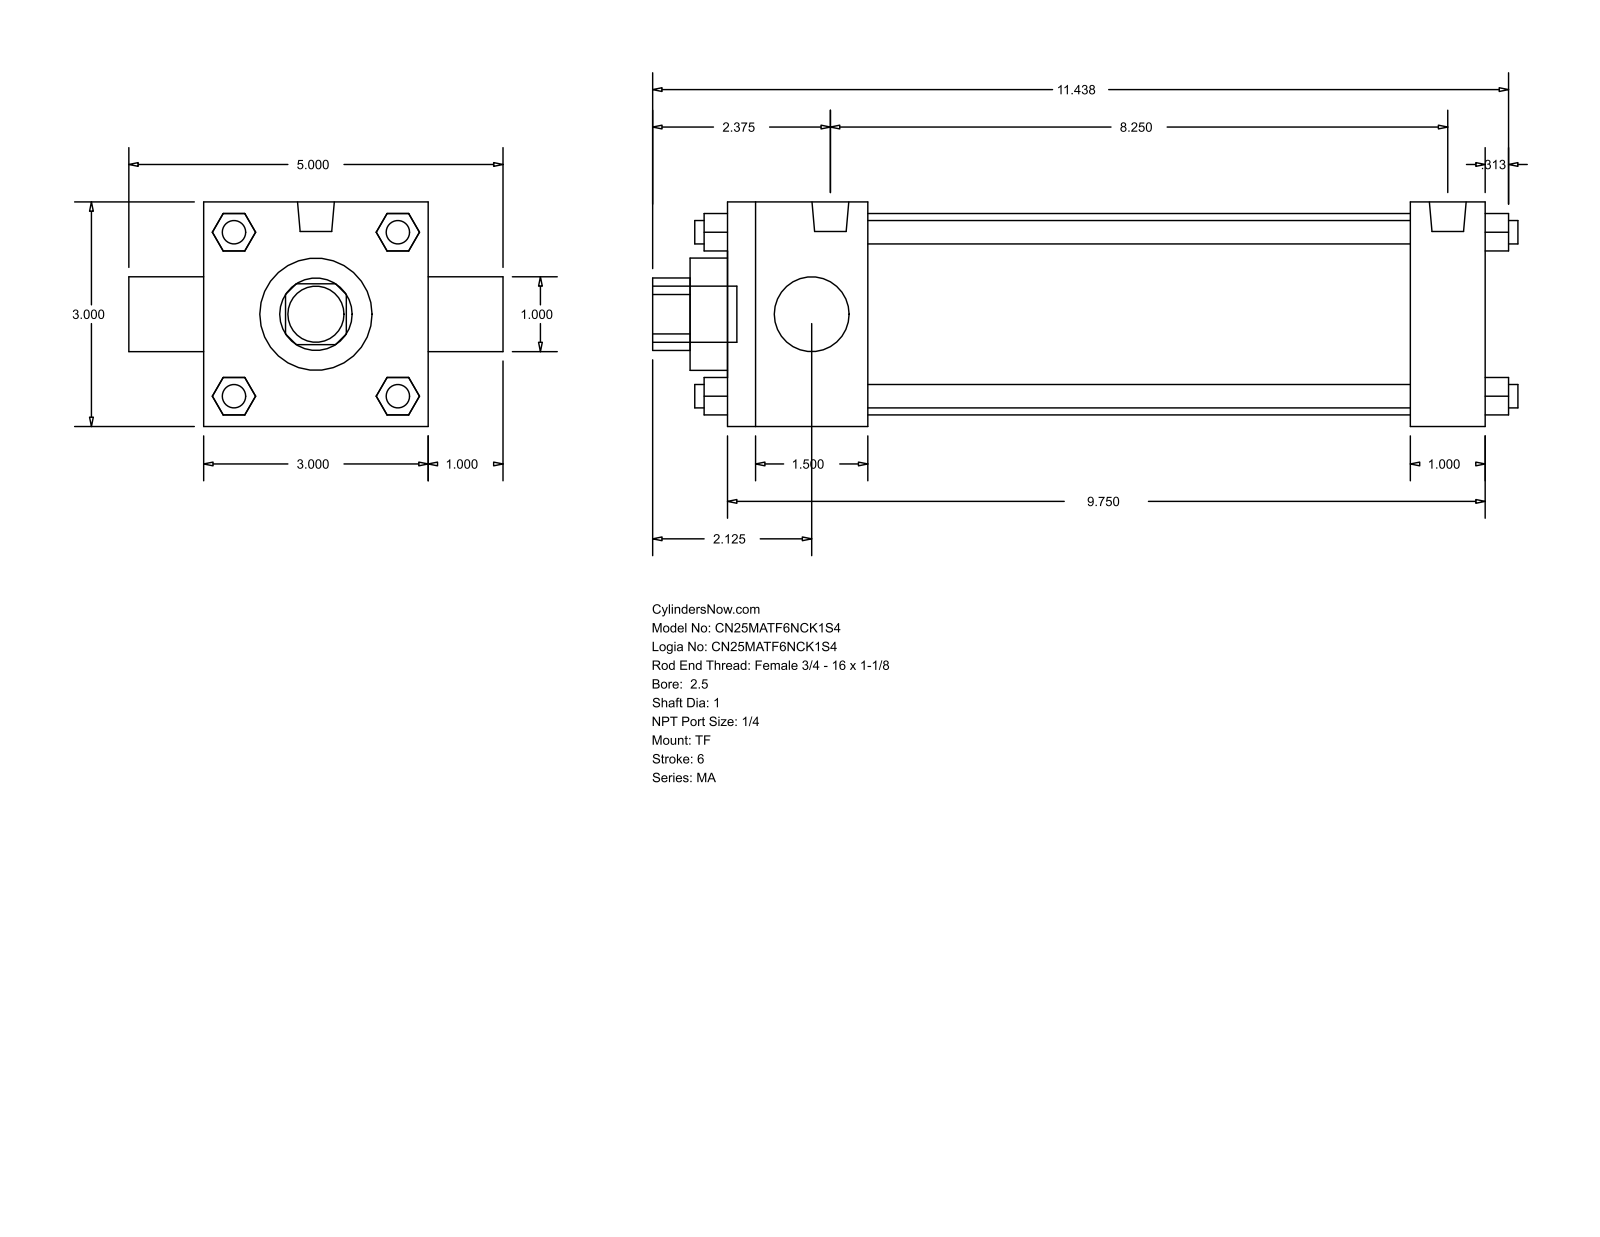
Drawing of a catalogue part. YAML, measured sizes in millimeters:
part_name: "MA_TF__0250_1"
step_written_by: "GSSL Pune (CONFIG_CONTROL_DESIGN)"
units: millimeters
bodies: {solids: 0, faces: 120, planar: 92, cylindrical: 28, other: 0}
overall_size: [293.69, 127, 76.2]
round_holes:
  - {diameter: 25.4, count: 2}
  - {diameter: 38.1, count: 1}
  - {diameter: 68.33, count: 1}
round_bosses_or_shafts:
  - {diameter: 7.94, count: 7}
  - {diameter: 12.49, count: 2}
  - {diameter: 19.05, count: 1}
partial_cylinders:
  - {radius: 12.29, count: 1}
face_to_face_distances: [76.2, 257.17, 12.7, 47.63, 231.78, 184.15, 209.54, 25.39, 25.4, 101.6]
